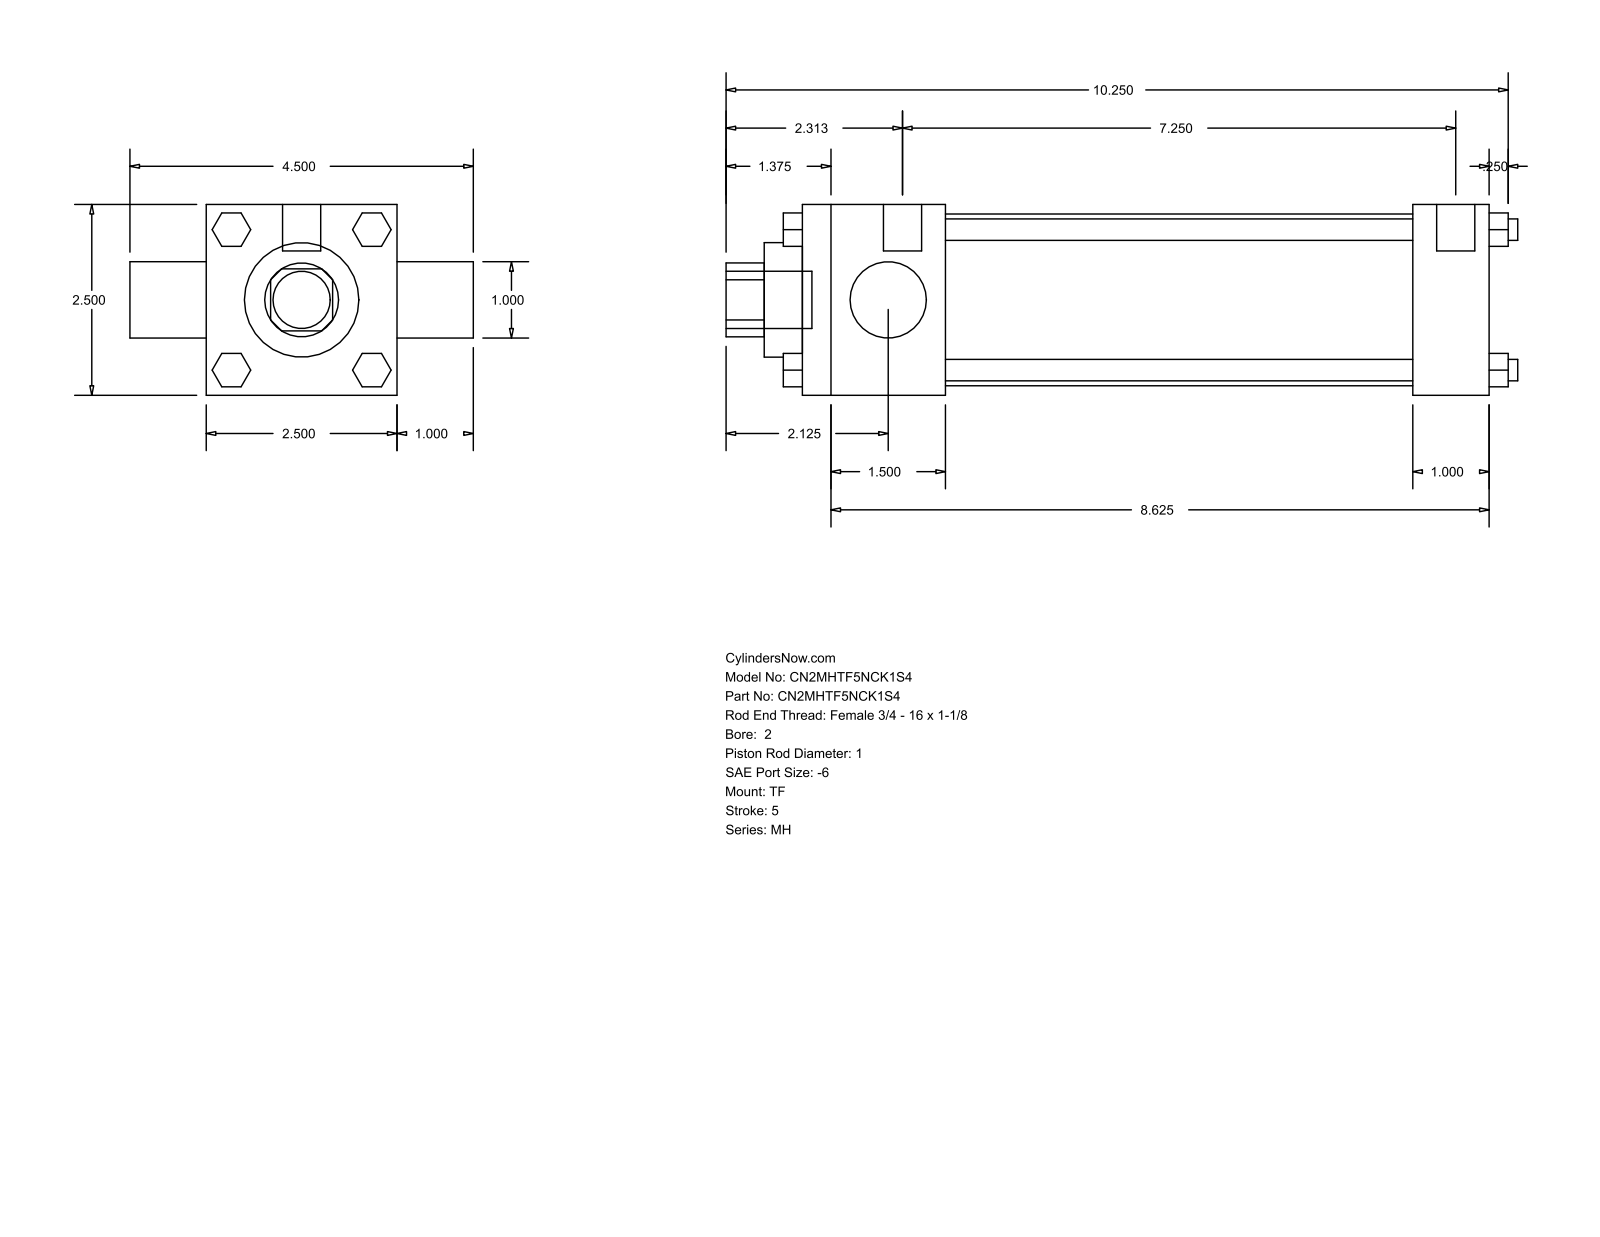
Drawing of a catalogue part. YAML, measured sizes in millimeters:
part_name: "MH_TF__0200_1"
step_written_by: "GSSL Pune (CONFIG_CONTROL_DESIGN)"
units: millimeters
bodies: {solids: 0, faces: 120, planar: 92, cylindrical: 28, other: 0}
overall_size: [263.52, 114.3, 63.5]
round_holes:
  - {diameter: 25.4, count: 2}
  - {diameter: 38.1, count: 1}
  - {diameter: 57.15, count: 1}
round_bosses_or_shafts:
  - {diameter: 7.14, count: 4}
  - {diameter: 5.56, count: 3}
  - {diameter: 12.7, count: 2}
  - {diameter: 19.05, count: 1}
partial_cylinders:
  - {radius: 12.29, count: 1}
face_to_face_distances: [63.5, 228.6, 25.4, 47.63, 203.2, 155.57, 180.97, 88.9, 241.3, 6.35]
